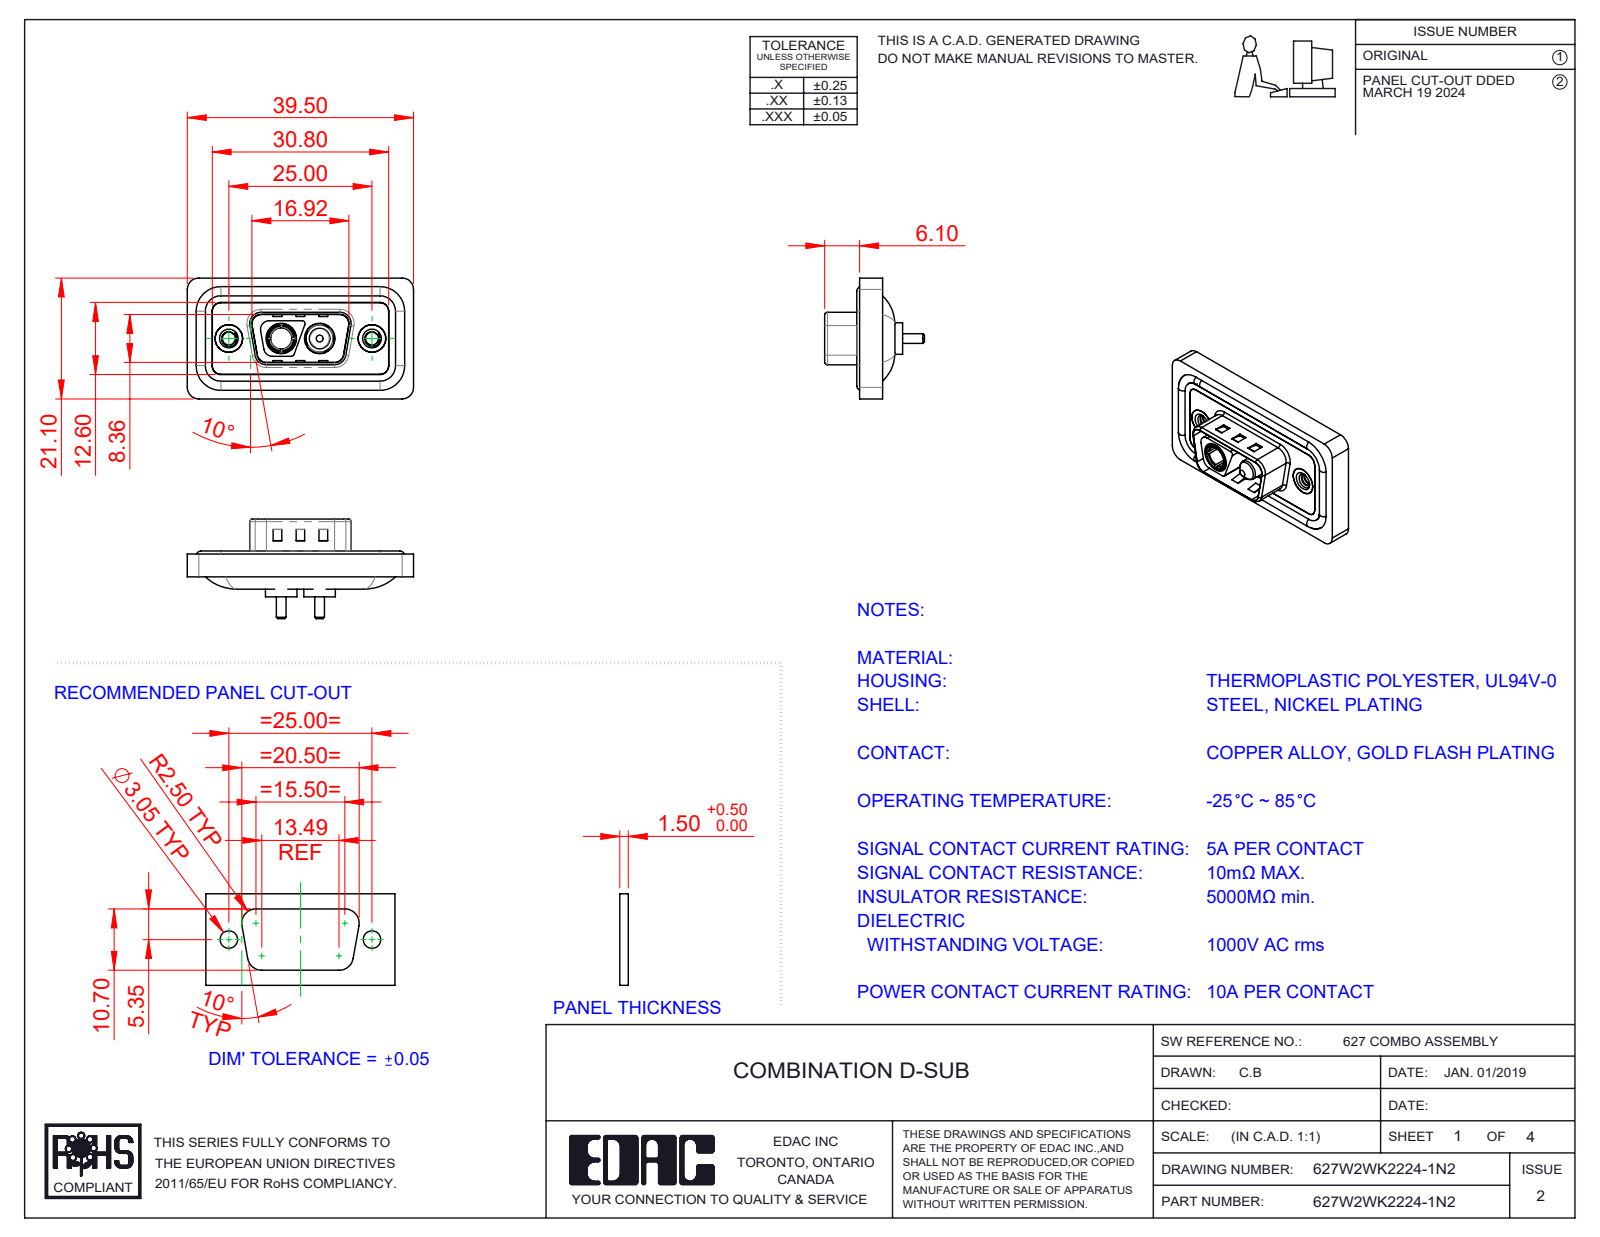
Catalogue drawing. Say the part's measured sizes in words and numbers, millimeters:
The part is named "627Combo Shell Rear_09 Contacts; 627W2WK2224-1N2; 627Combo Housing_2WK2; 627Combo Threaded Rivet_2 (+4 more)". Its 3-D file was written by "SolidWorks 2023 (CONFIG_CONTROL_DESIGN)". It is 11 solids with 534 faces: 189 planar, 227 cylindrical and 118 other. Overall it measures 39.5 by 21.1 by 17.4 millimeters. Its volume is 4 525 cubic millimeters and its surface area 7 317 square millimeters. Round holes: 2 of diameter 2.26, 2 of diameter 4, 2 of diameter 4.8, 2 of diameter 4.85, 2 of diameter 5, 2 of diameter 5.3, 1 of diameter 3.7. Round bosses or shafts: 4 of diameter 1.6, 2 of diameter 5.5, 2 of diameter 5.2, 2 of diameter 4.9, 2 of diameter 4.75, 2 of diameter 3.75, 2 of diameter 1.7, 1 of diameter 4.96. Partial cylindrical surfaces (rounded edges, fillets, slot ends): 24 of radius 1.5, 18 of radius 2, 10 of radius 0.5, 8 of radius 1.6, 4 of radius 0.25, 4 of radius 0.6, 4 of radius 0.65, 4 of radius 0.9. The main face-to-face distances are 0.4, 1.1, 2.9, 0.5, 3.1, 1.6, 1.5, 4, 2.5, 1.8. The hole center spacings are 9.14, 15.86, 6.72, 25.
